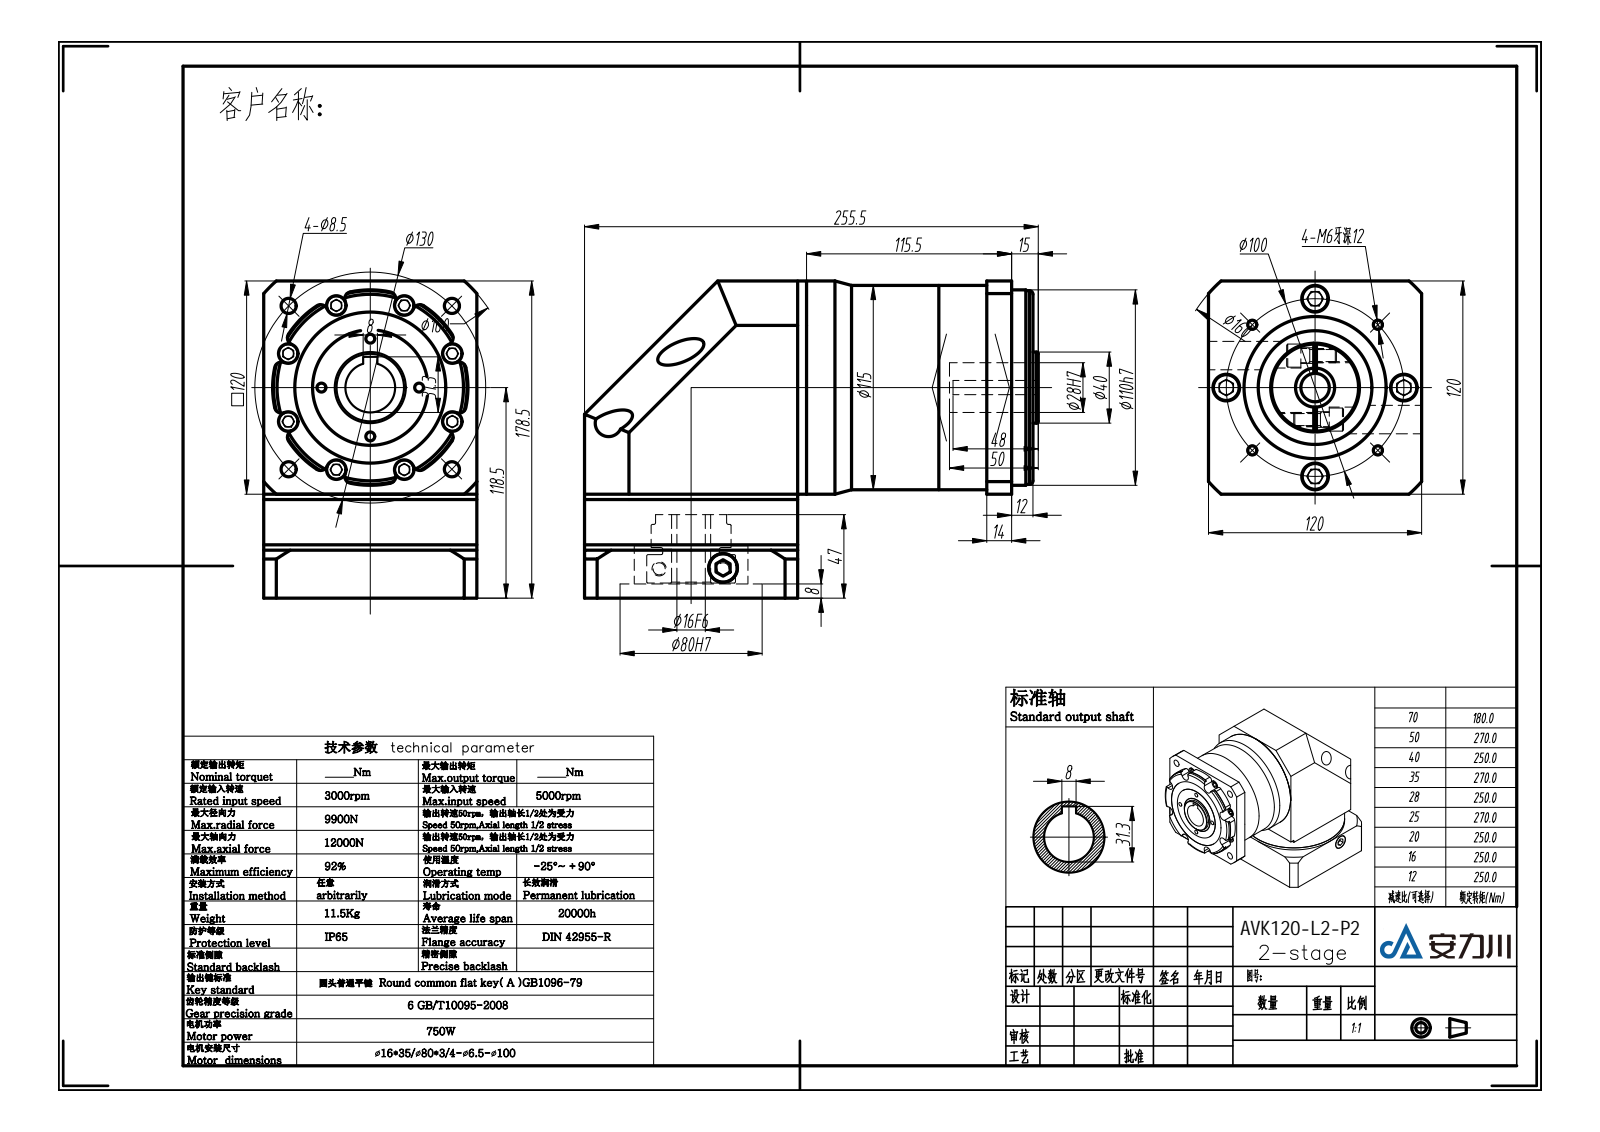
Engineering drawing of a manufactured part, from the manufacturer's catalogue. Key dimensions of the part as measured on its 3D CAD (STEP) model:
Part name (STEP PRODUCT): VGZK115双级模型（16-35 80-3 4-6.5-100）
STEP written by: SolidWorks 2016 (AUTOMOTIVE_DESIGN)
Units: millimetres
Bodies: 23 solids, 504 faces (279 planar, 200 cylindrical, 25 other)
Overall size (bounding box): 255.5 × 178.5 × 120
Volume: 3 263 000 mm³ · Surface area: 343 489 mm²
Round holes (diameter × count): ⌀15 ×10, ⌀5 ×8, ⌀11 ×8, ⌀8.5 ×4, ⌀16 ×3, ⌀20 ×1, ⌀22 ×1, ⌀28 ×1, ⌀45.2 ×1, ⌀70 ×1, ⌀80 ×1, ⌀85 ×1
Round bosses / shafts (diameter × count): ⌀13 ×10, ⌀9.5 ×8, ⌀120 ×2, ⌀15.6 ×2, ⌀115 ×1, ⌀65 ×1, ⌀50 ×1, ⌀45 ×1
Partial cylindrical surfaces — rounded edges, fillets, slot ends (radius × count): R4 ×16, R80 ×2, R54.5 ×1, R55 ×1
Main face-to-face distances: 5, 25.5, 120, 49.17, 74.5, 79.5, 25.33, 30.33, 30, 55.5
Hole centre spacings: 38.27, 39.29, 94.69, 26.74, 26.83, 46.94, 49.53, 49.99
